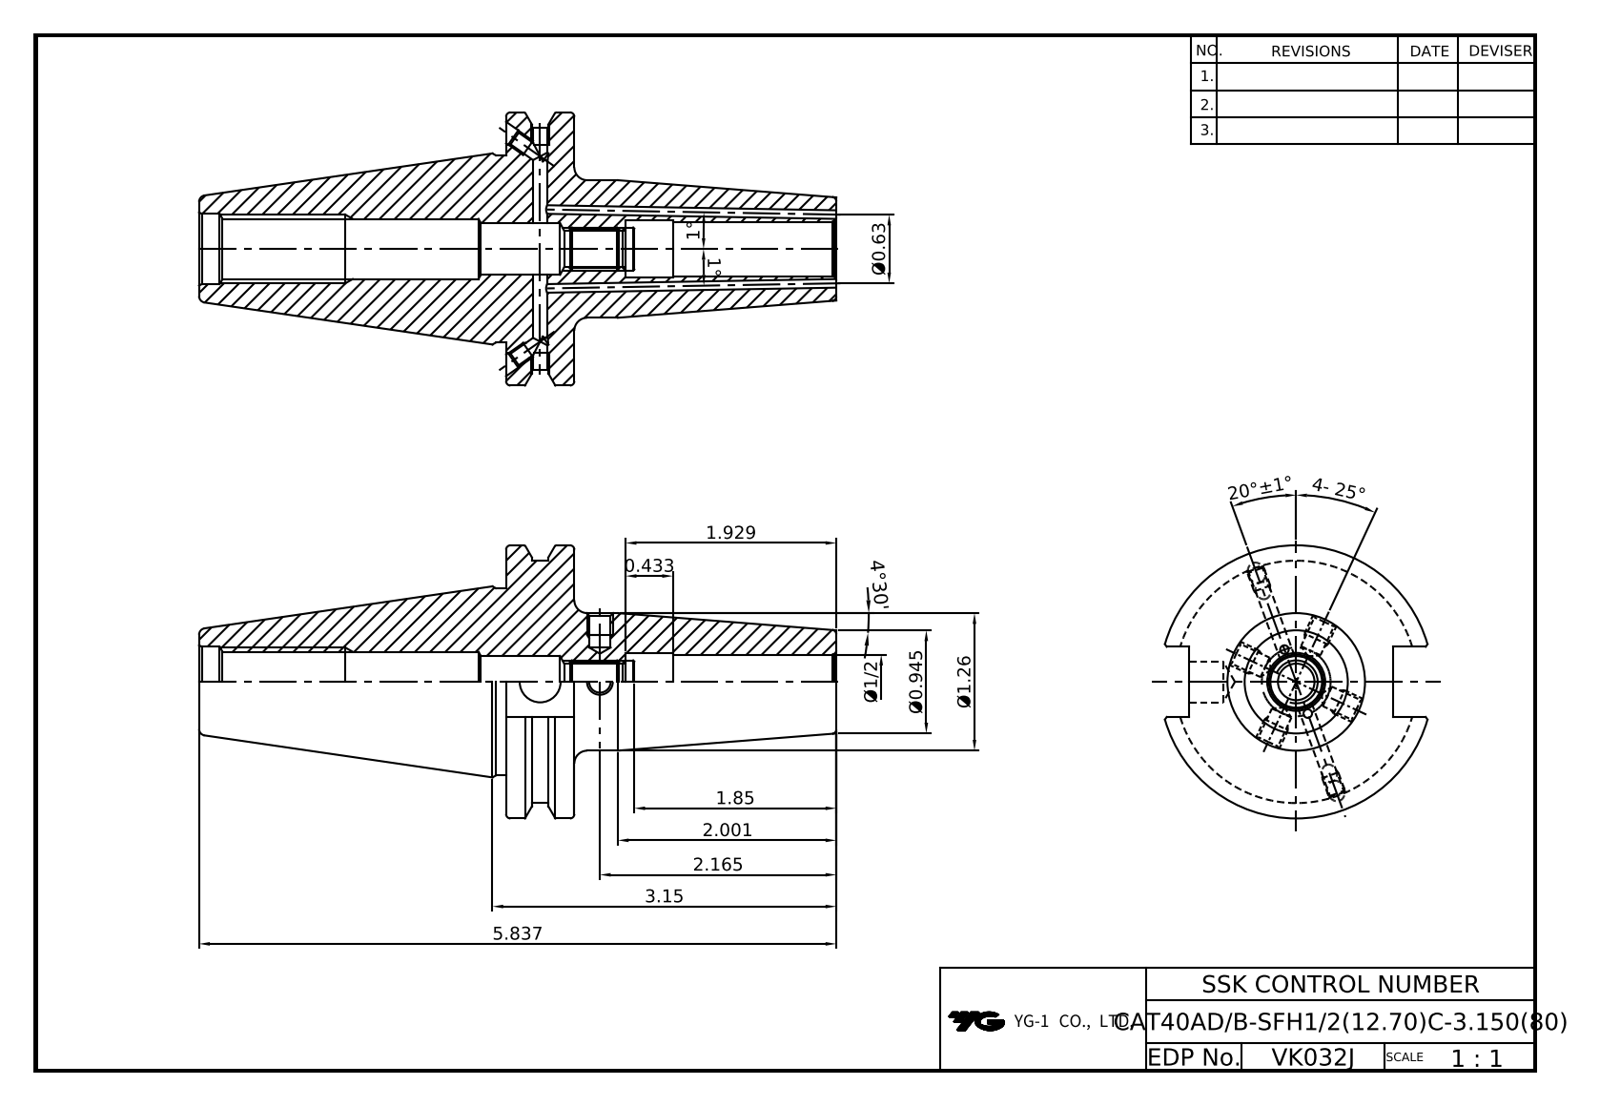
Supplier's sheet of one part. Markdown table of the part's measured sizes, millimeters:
| quantity | value |
| --- | --- |
| part name | LO-CAT40ADB-SFH12.7C-80 |
| STEP written by | Autodesk Inventor 2024 (AUTOMOTIVE_DESIGN) |
| units | millimeters |
| bodies | 1 solid, 91 faces (39 planar, 31 cylindrical, 21 other) |
| overall size | 148.25 × 63.5 × 61.09 |
| volume | 133 193 mm³ |
| surface area | 28 803 mm² |
| round holes (diameter × count) | 3.24 × 4, 2.5 × 2, 4 × 2, 4.2 × 2, 8.92 × 1, 9.53 × 1, 12.7 × 1, 13 × 1, 13.39 × 1, 13.9 × 1, 16.3 × 1 |
| round bosses / shafts (diameter × count) | 63.5 × 1, 43.6 × 1, 32 × 1 |
| partial cylindrical surfaces (radius × count) | 28.15 × 1 |
| main face-to-face distances | 15.88, 76.83, 60.95, 47.6, 16.38, 71.42, 87.3, 148.25, 77.47, 6.05 |
